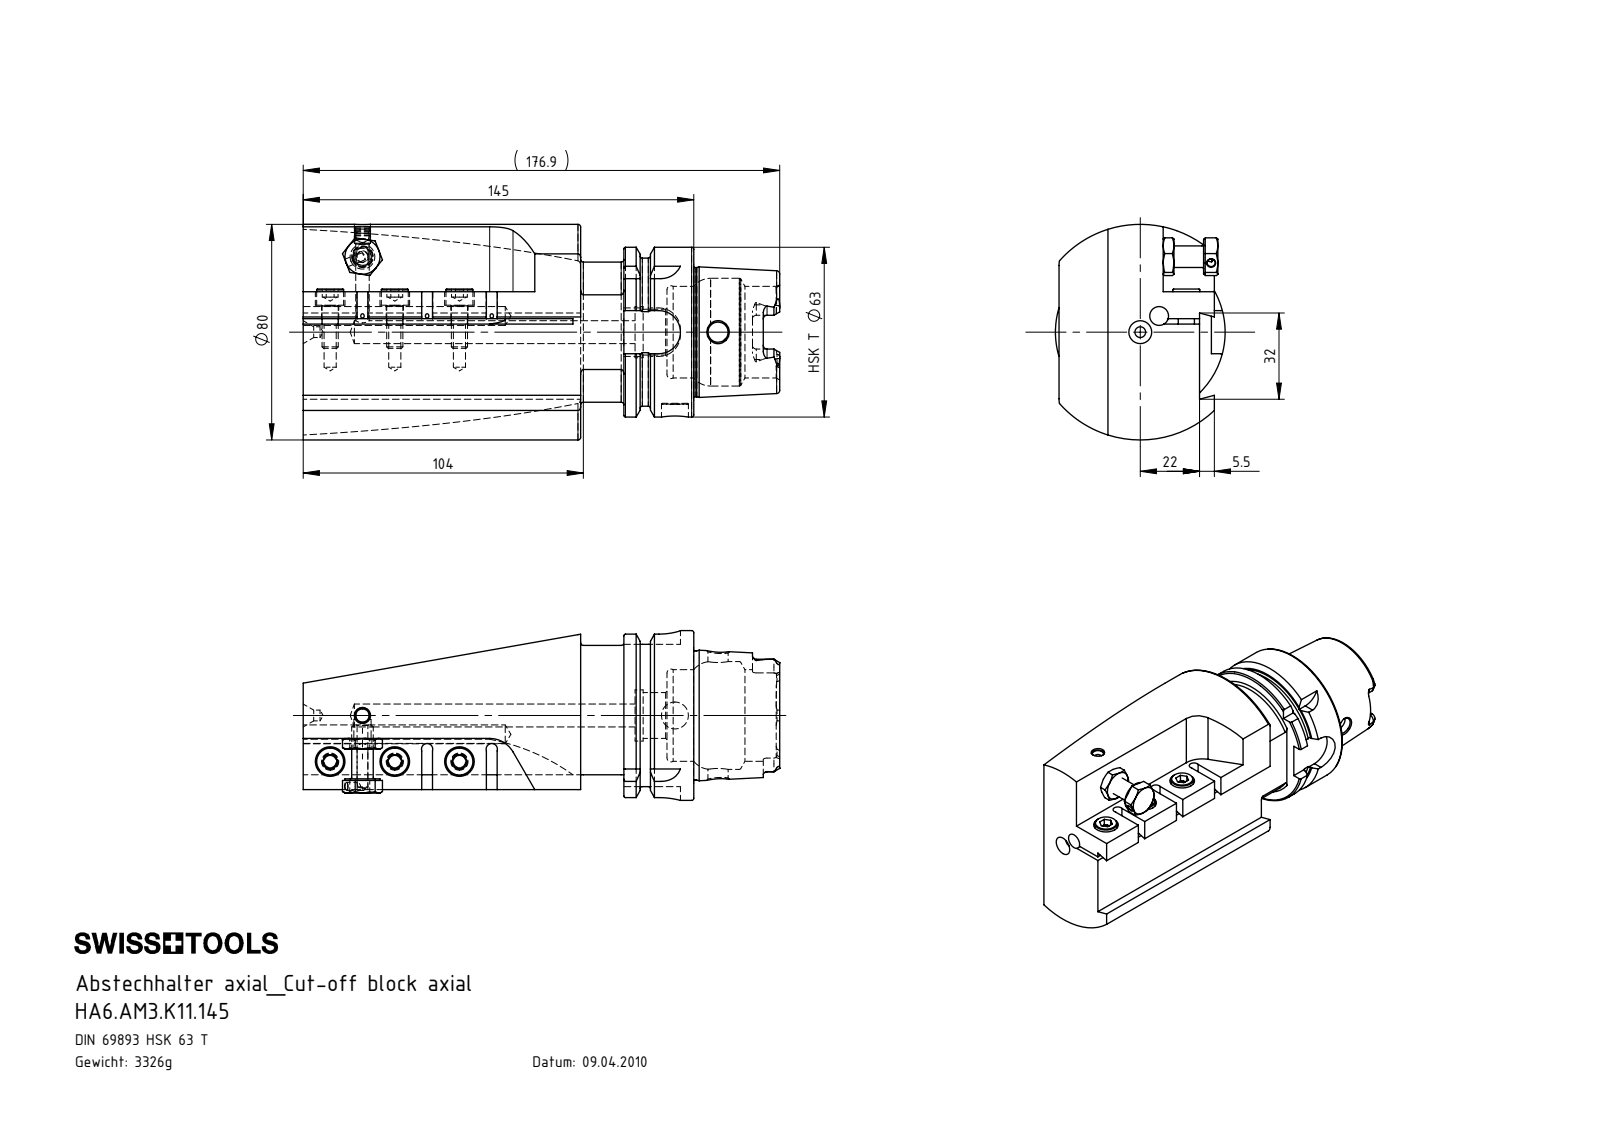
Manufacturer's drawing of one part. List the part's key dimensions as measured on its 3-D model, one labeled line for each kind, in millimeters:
Part name (STEP PRODUCT): ISO 4762 - M6 x 16_PreviewCfg; KVT_MB_600_060; AM3-ER1.001.020_PreviewCfg; HA6-AM3.K11.145_C_Fertigbearbeitung (+2 more)
STEP written by: SolidWorks 2017 (AUTOMOTIVE_DESIGN)
Units: millimetres
Bodies: 8 solids, 436 faces (146 planar, 113 cylindrical, 177 other)
Overall size (bounding box): 176.9 × 80 × 63
Volume: 424 934 mm³ · Surface area: 66 031 mm²
Round holes (diameter × count): ⌀6.4 ×4, ⌀4.5 ×3, ⌀11 ×3, ⌀4 ×2, ⌀7 ×2, ⌀3 ×1, ⌀5 ×1, ⌀7.5 ×1, ⌀8.5 ×1, ⌀10 ×1, ⌀17 ×1, ⌀19 ×1
Round bosses / shafts (diameter × count): ⌀6 ×4, ⌀10 ×3, ⌀63 ×1, ⌀54.95 ×1, ⌀52 ×1, ⌀47.94 ×1, ⌀13 ×1, ⌀8 ×1
Partial cylindrical surfaces — rounded edges, fillets, slot ends (radius × count): R1.4 ×6, R2.88 ×4, R8 ×4, R2.1 ×3, R10 ×1, R40 ×1, R77.5 ×1
Main face-to-face distances: 13.5, 19, 103, 5.5, 12, 42, 145, 2, 10, 24
Hole centre spacings: 20.89, 24, 9.22, 39.85, 48, 81.81, 105.4, 116
